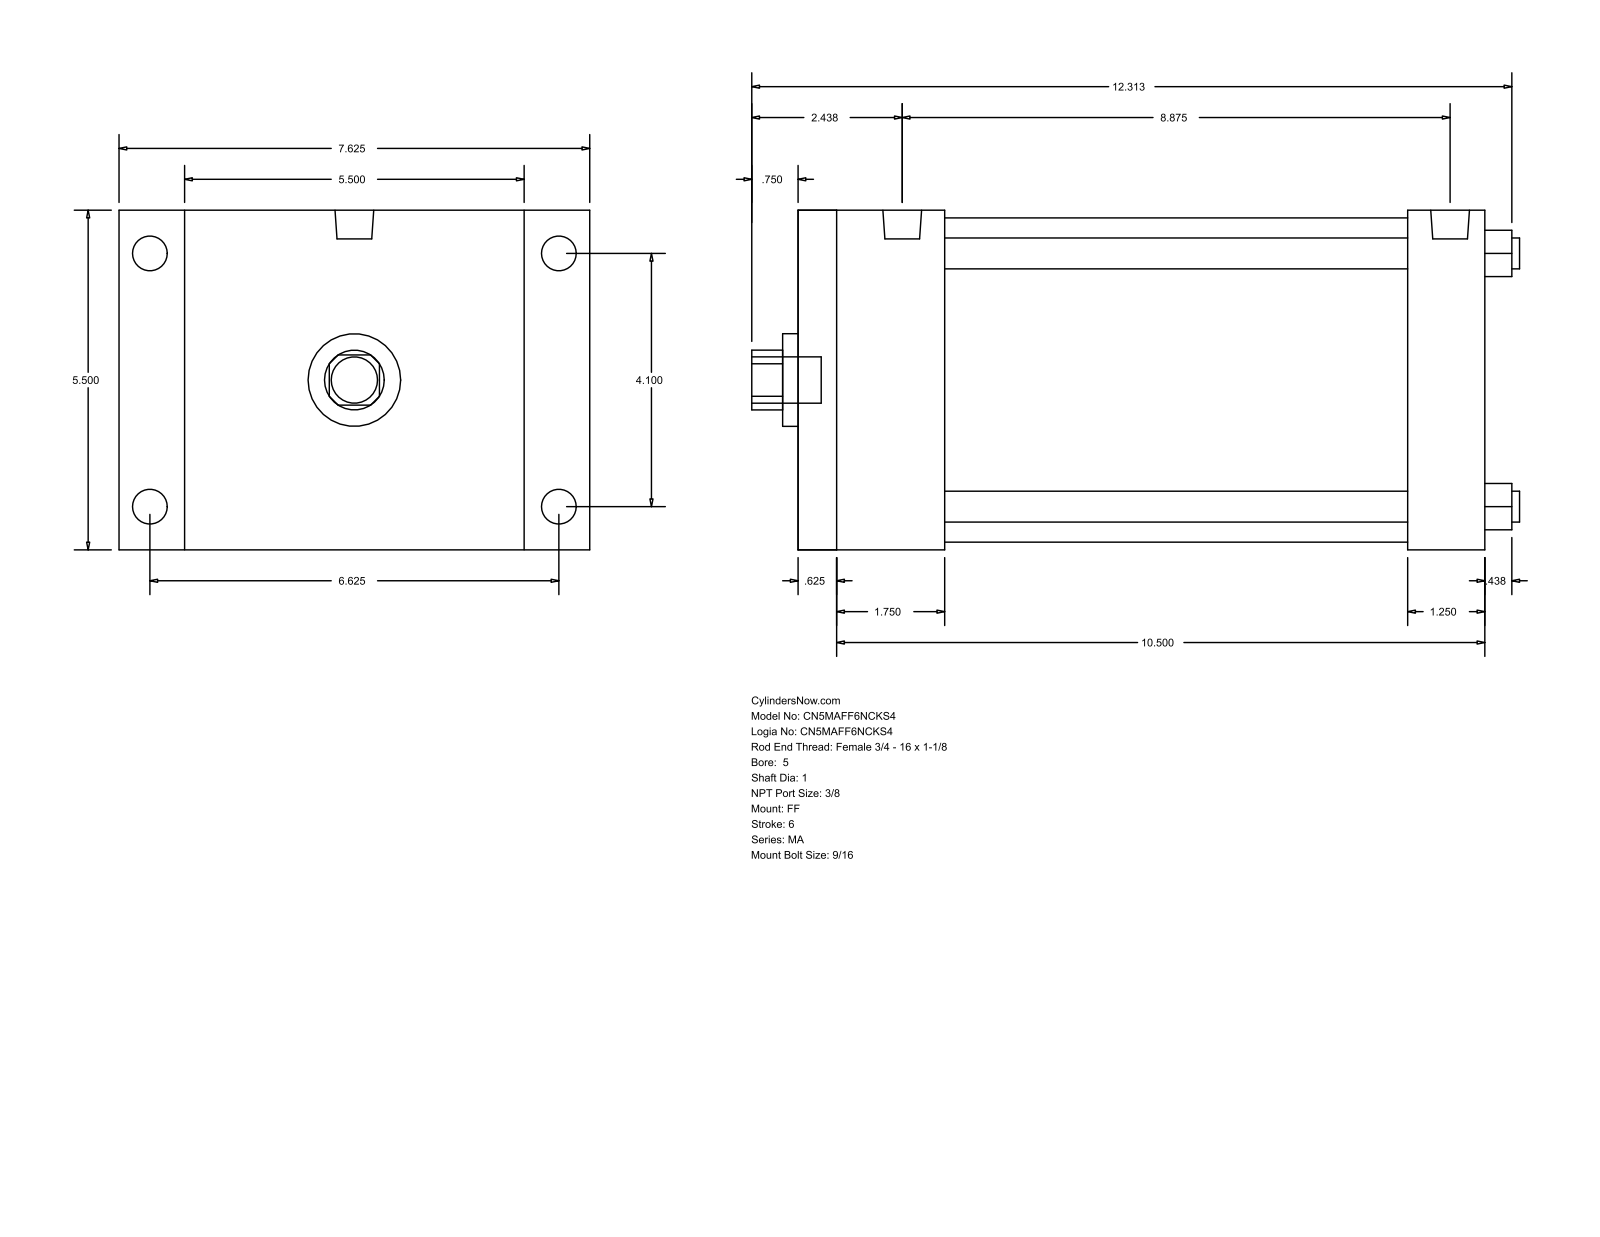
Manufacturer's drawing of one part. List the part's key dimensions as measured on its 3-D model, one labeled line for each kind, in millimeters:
Part name (STEP PRODUCT): MA_FF__0500_1
STEP written by: GSSL Pune (CONFIG_CONTROL_DESIGN)
Units: millimetres
Bodies: 0 solids, 92 faces (64 planar, 28 cylindrical, 0 other)
Overall size (bounding box): 315.91 × 193.68 × 139.7
Round holes (diameter × count): ⌀12.7 ×4, ⌀25.4 ×1, ⌀38.1 ×1, ⌀133.35 ×1
Round bosses / shafts (diameter × count): ⌀14.29 ×4, ⌀11.11 ×4, ⌀15.93 ×2, ⌀19.05 ×1
Partial cylindrical surfaces — rounded edges, fillets, slot ends (radius × count): R12.29 ×1
Main face-to-face distances: 139.7, 282.57, 15.87, 266.7, 250.83, 234.96, 31.74, 60.33, 44.46, 190.5
Hole centre spacings: 73.64, 104.14, 147.28
